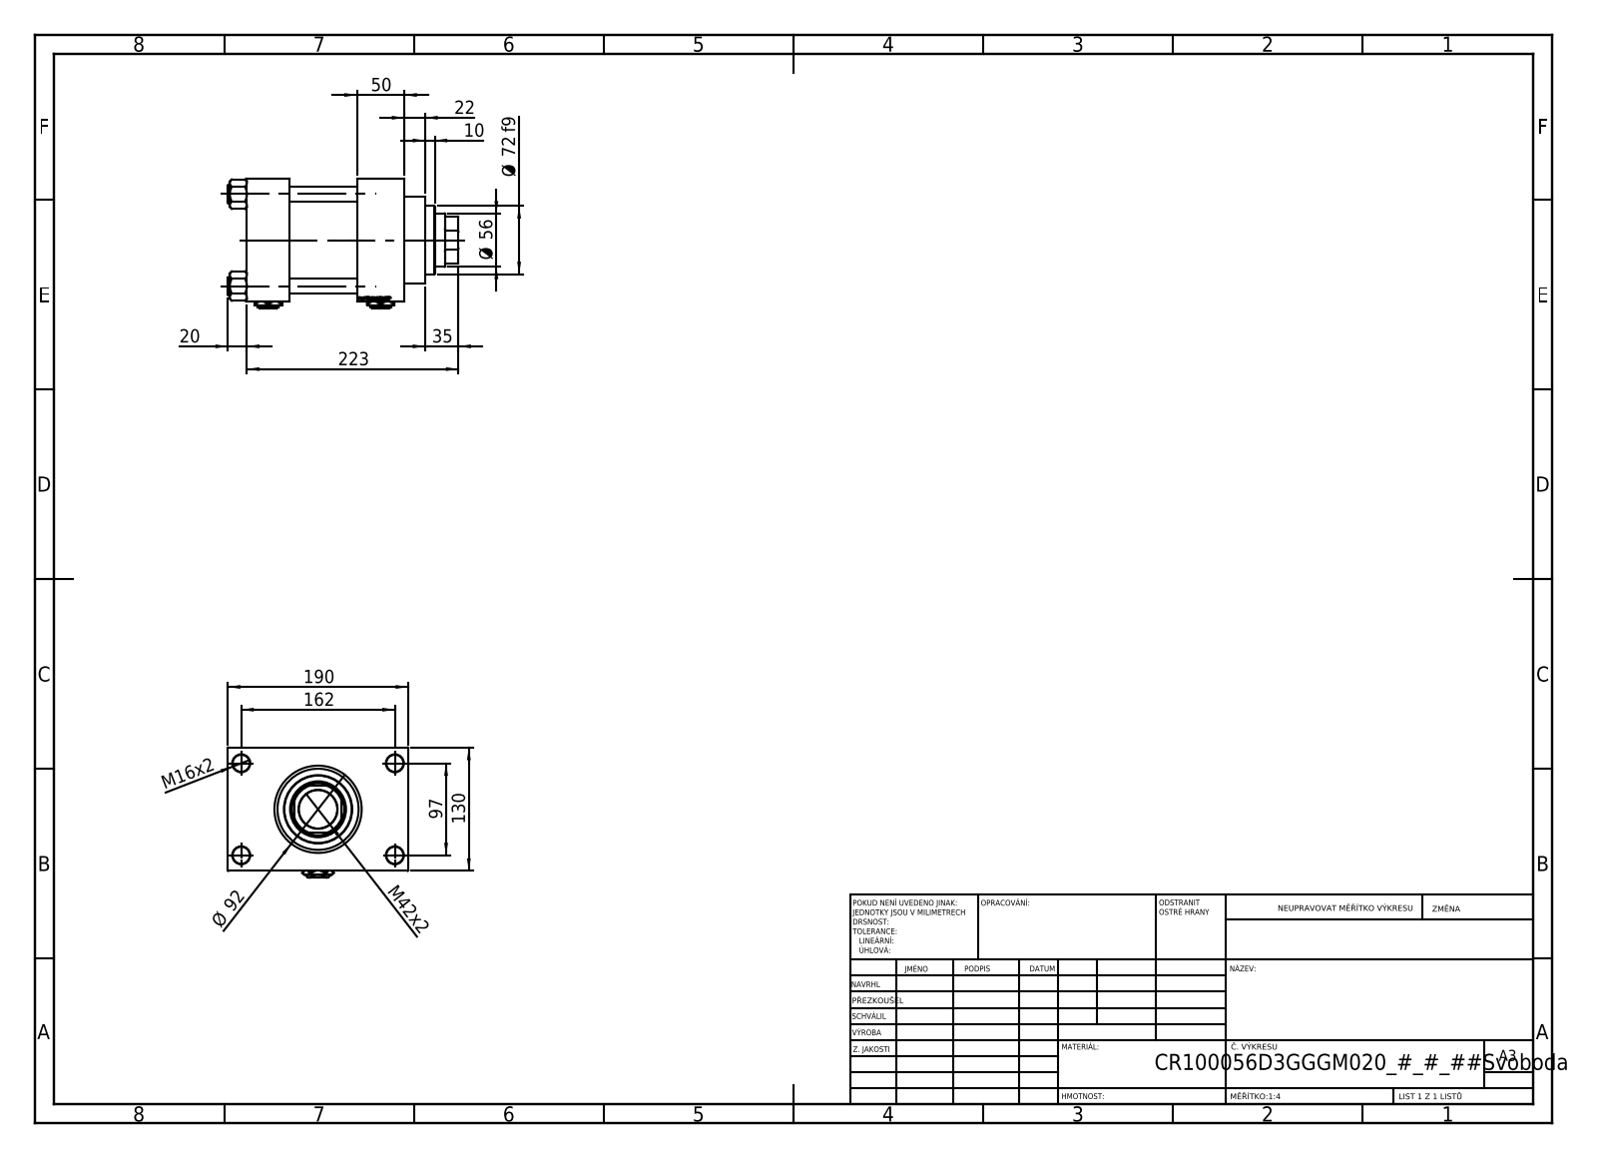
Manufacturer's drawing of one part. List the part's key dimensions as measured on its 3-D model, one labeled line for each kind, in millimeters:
Part name (STEP PRODUCT): V215_VC_A; V215CR_D_TYCINKA; V215CR_VCP_D; NUT_M5_D (+2 more)
STEP written by: SolidWorks 2019 (CONFIG_CONTROL_DESIGN)
Units: millimetres
Bodies: 13 solids, 1253 faces (593 planar, 100 cylindrical, 560 other)
Overall size (bounding box): 243 × 190 × 137
Volume: 2 630 000 mm³ · Surface area: 366 798 mm²
Round holes (diameter × count): ⌀16 ×4, ⌀18 ×4, ⌀7 ×2, ⌀26.44 ×2, ⌀35 ×2, ⌀40.5 ×1, ⌀56 ×1, ⌀59 ×1, ⌀76 ×1, ⌀85.5 ×1, ⌀100 ×1
Round bosses / shafts (diameter × count): ⌀19 ×4, ⌀106 ×1, ⌀92 ×1, ⌀72 ×1
Partial cylindrical surfaces — rounded edges, fillets, slot ends (radius × count): R27 ×1
Main face-to-face distances: 130, 116, 50, 45, 71, 121, 166, 30, 160, 190
Hole centre spacings: 32.55, 68.52, 94.41, 96.9, 102.27, 129.45, 161.73, 97
